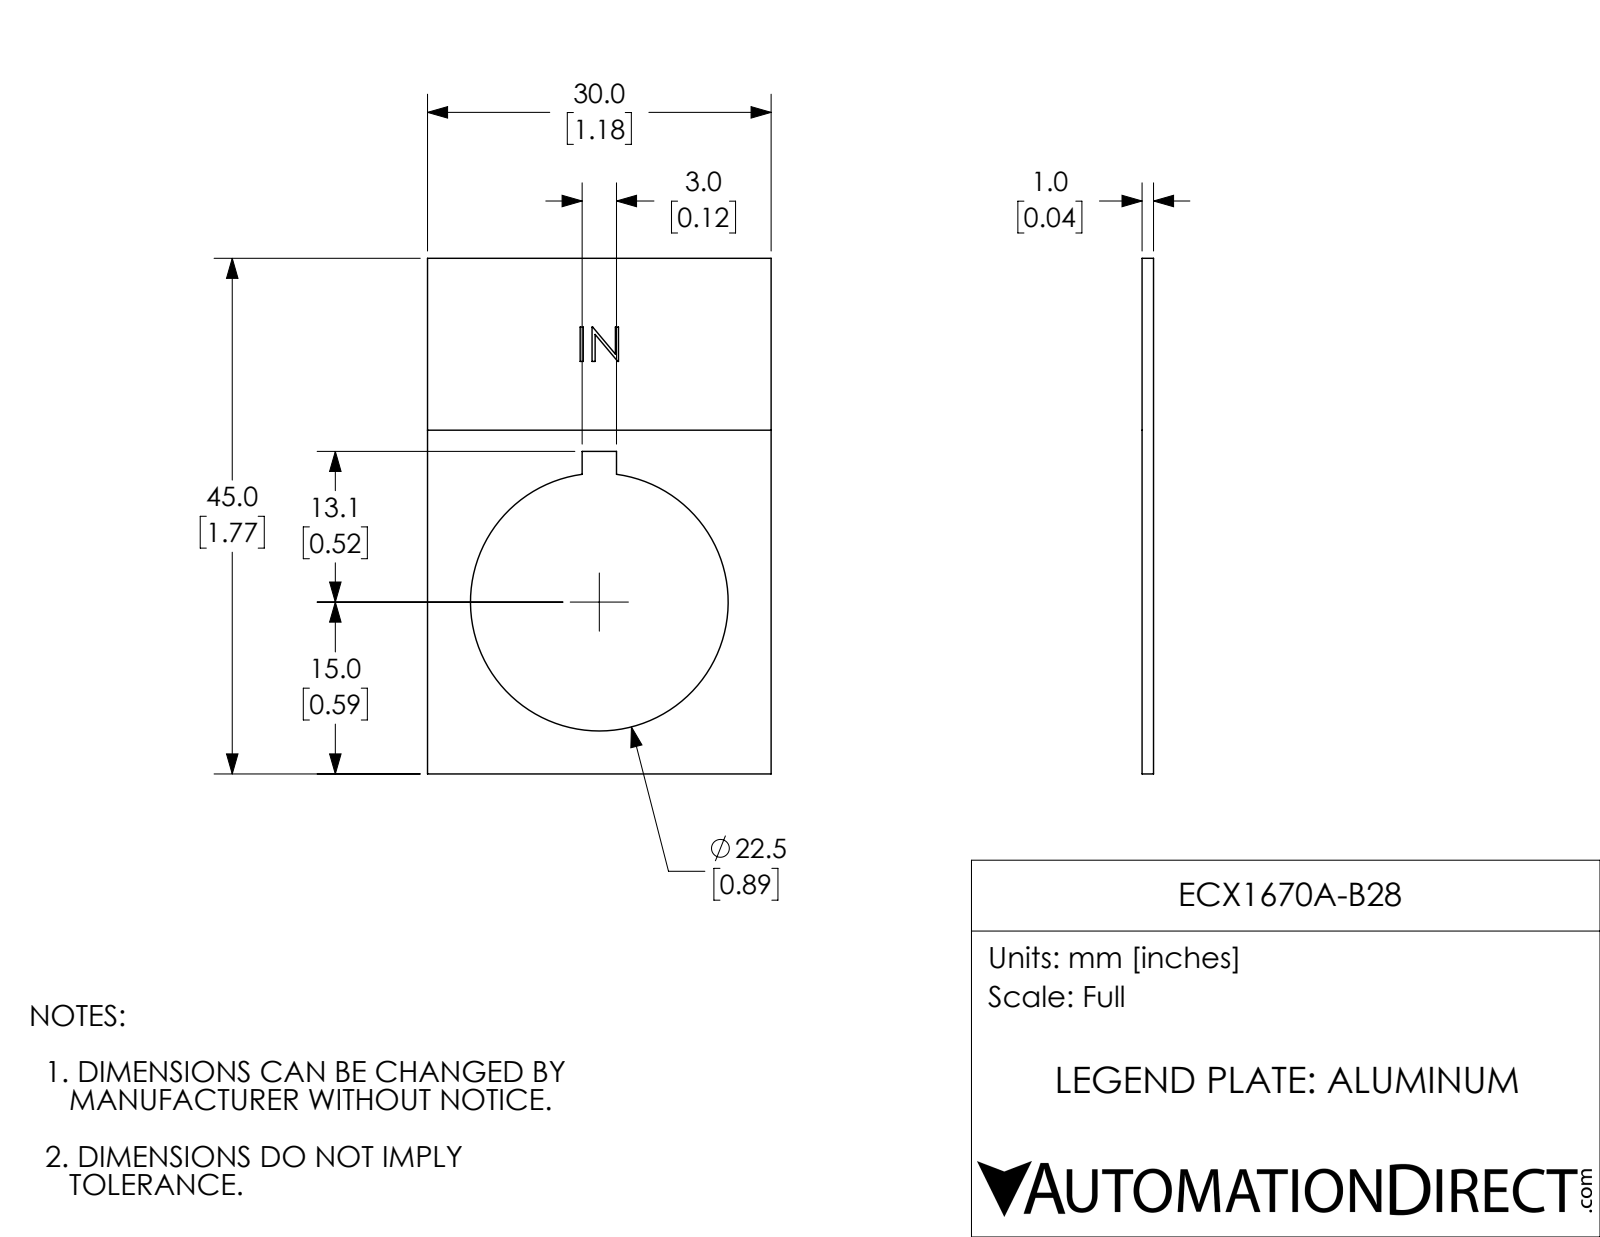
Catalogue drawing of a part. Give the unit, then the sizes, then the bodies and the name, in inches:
Units: inches
Overall size (bounding box): 1.772 × 1.181 × 0.039
Round holes (diameter × count): ⌀0.886 ×1
Main face-to-face distances: 0.039, 1.181, 1.772, 0.531, 0.65, 0.038, 1.108, 0.663, 0.118, 0.525
Volume: 0.058 in³ · Surface area: 3.284 in²
Bodies: 1 solid, 29 faces (26 planar, 3 cylindrical, 0 other)
Part name (STEP PRODUCT): ECX1670A-B28
STEP written by: SolidWorks 2017 (AUTOMOTIVE_DESIGN)
